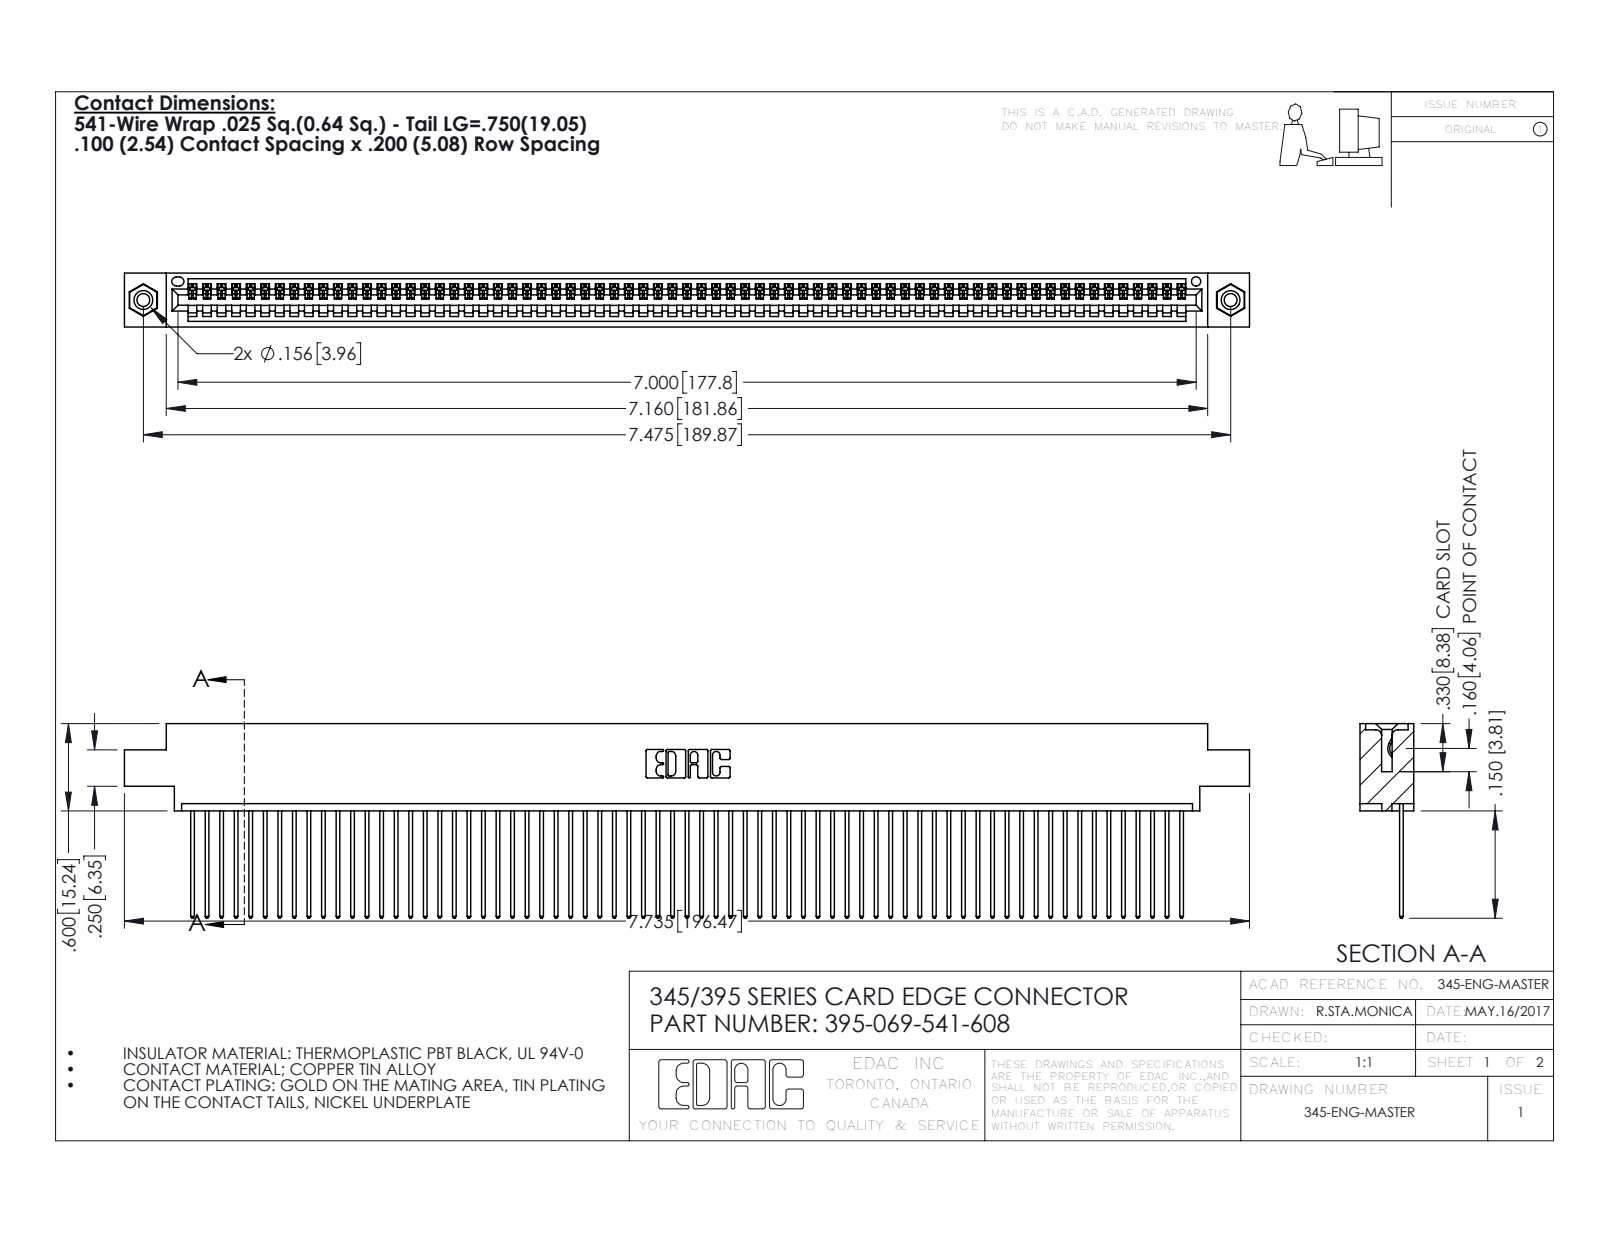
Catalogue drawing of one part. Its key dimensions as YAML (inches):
part_name: "395-069-541-608; 345 Part_0.170 Offset - 0.156 Dia-TI; 345-292-001_345-293-141; 345-250-001_345-250-003-102"
step_written_by: "SolidWorks 2016 (CONFIG_CONTROL_DESIGN)"
units: inches
bodies: {solids: 72, faces: 4192, planar: 2876, cylindrical: 1300, other: 16}
overall_size: [7.735, 1.337, 0.37]
volume: 1.159
surface_area: 41.99
round_holes:
  - {diameter: 0.089, count: 2}
  - {diameter: 0.125, count: 2}
  - {diameter: 0.156, count: 2}
  - {diameter: 0.064, count: 1}
round_bosses_or_shafts:
  - {diameter: 0.155, count: 2}
partial_cylinders:
  - {radius: 0.006, count: 138}
  - {radius: 0.01, count: 138}
  - {radius: 0.01, count: 22}
  - {radius: 0.007, count: 6}
  - {radius: 0.031, count: 6}
  - {radius: 0.026, count: 3}
  - {radius: 0.031, count: 2}
  - {radius: 0.04, count: 2}
face_to_face_distances: [0.072, 0.298, 0.098, 0.272, 0.025, 0.37, 0.2, 0.225, 0.175, 0.149]
hole_center_spacings: [0.27, 7.239, 7.475]
